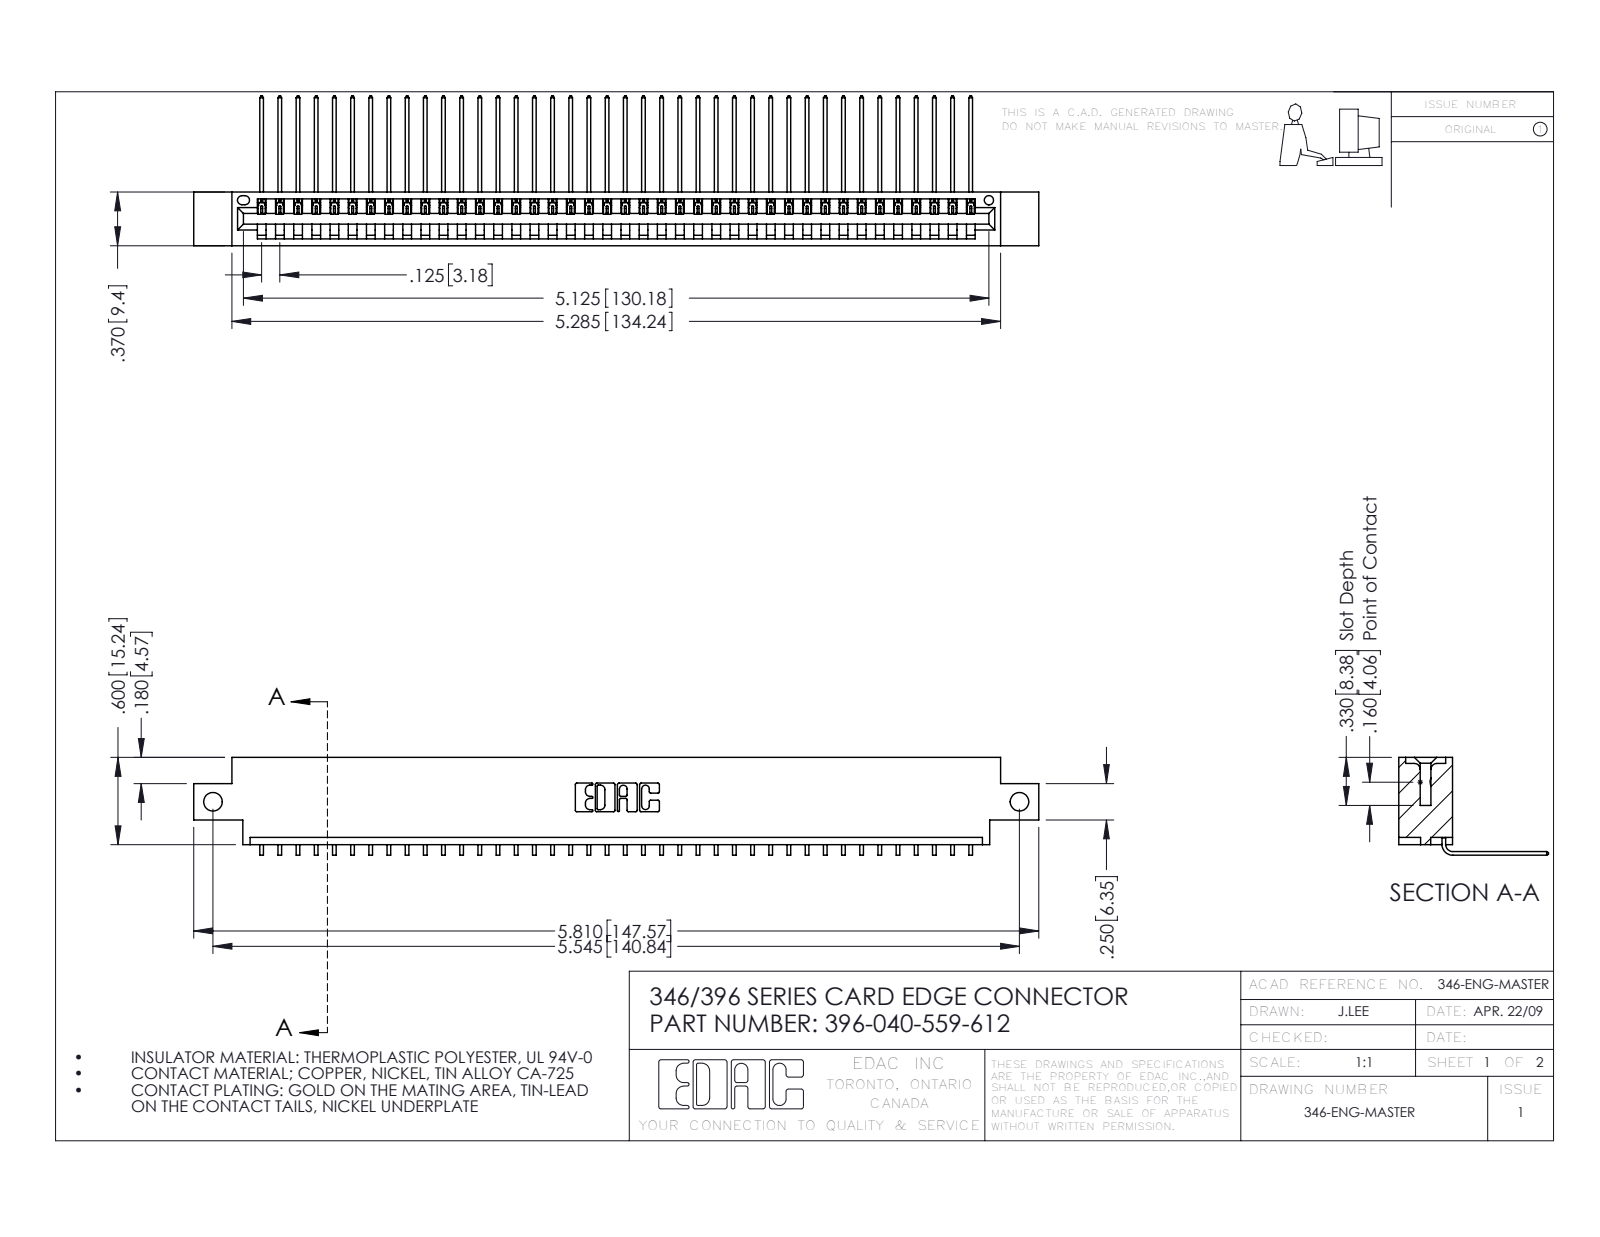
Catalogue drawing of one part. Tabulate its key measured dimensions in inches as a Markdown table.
| quantity | value |
| --- | --- |
| part name | 345-292-001_558 559 Tail - 1; 346 Part_0.170 Offset - Side Mount; 396-040-559-612 |
| STEP written by | SolidWorks 2016 (CONFIG_CONTROL_DESIGN) |
| units | inches |
| bodies | 41 solids, 2526 faces (1760 planar, 766 cylindrical, 0 other) |
| overall size | 5.81 × 1.03 × 0.673 |
| volume | 0.855 in³ |
| surface area | 28.35 in² |
| round holes (diameter × count) | 0.128 × 2, 0.064 × 1 |
| partial cylindrical surfaces (radius × count) | 0.006 × 80, 0.01 × 22, 0.007 × 6, 0.031 × 6, 0.026 × 3, 0.031 × 2, 0.04 × 2, 0.014 × 1 |
| main face-to-face distances | 0.048, 0.322, 0.37, 0.25, 0.025, 0.072, 0.298, 0.148, 0.222, 0.1 |
| hole center spacings | 5.545 |
